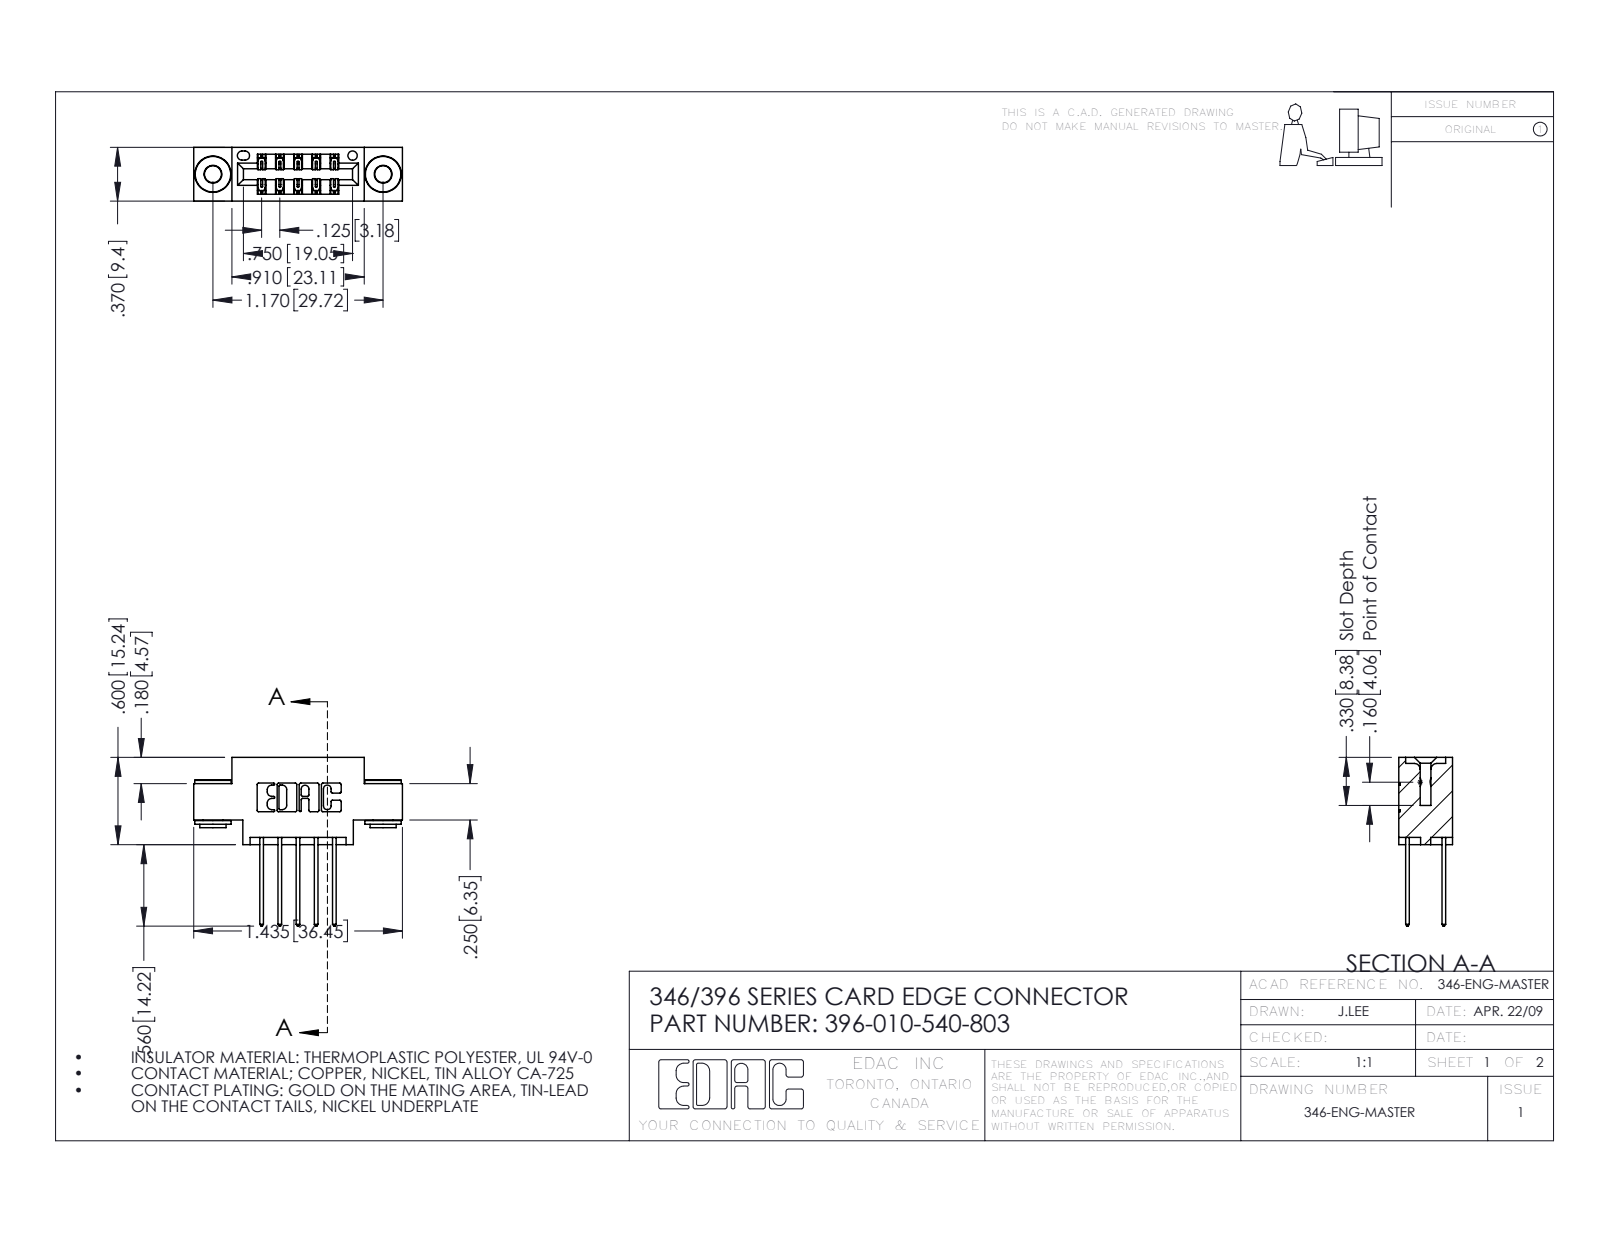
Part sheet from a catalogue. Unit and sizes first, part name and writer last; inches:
Units: inches
Overall size (bounding box): 1.435 × 1.16 × 0.37
Round holes (diameter × count): ⌀0.116 ×2, ⌀0.156 ×2, ⌀0.064 ×1
Round bosses / shafts (diameter × count): ⌀0.25 ×2, ⌀0.18 ×2, ⌀0.136 ×2
Partial cylindrical surfaces — rounded edges, fillets, slot ends (radius × count): R0.01 ×22, R0.006 ×15, R0.01 ×10, R0.007 ×6, R0.031 ×6, R0.026 ×3, R0.014 ×2, R0.022 ×2
Main face-to-face distances: 0.25, 0.37, 0.048, 0.322, 0.025, 0.072, 0.298, 0.275, 0.225, 0.148
Hole centre spacings: 0.246, 0.969, 1.17
Volume: 0.193 in³ · Surface area: 6.74 in²
Bodies: 13 solids, 684 faces (440 planar, 236 cylindrical, 8 other)
Part name (STEP PRODUCT): 396-010-540-803; 346 Part_0.170 Offset - 0.156 Dia-TH; 345-292-001_345-293-140; 345-250-002_345-250-002-102
STEP written by: SolidWorks 2016 (CONFIG_CONTROL_DESIGN)
